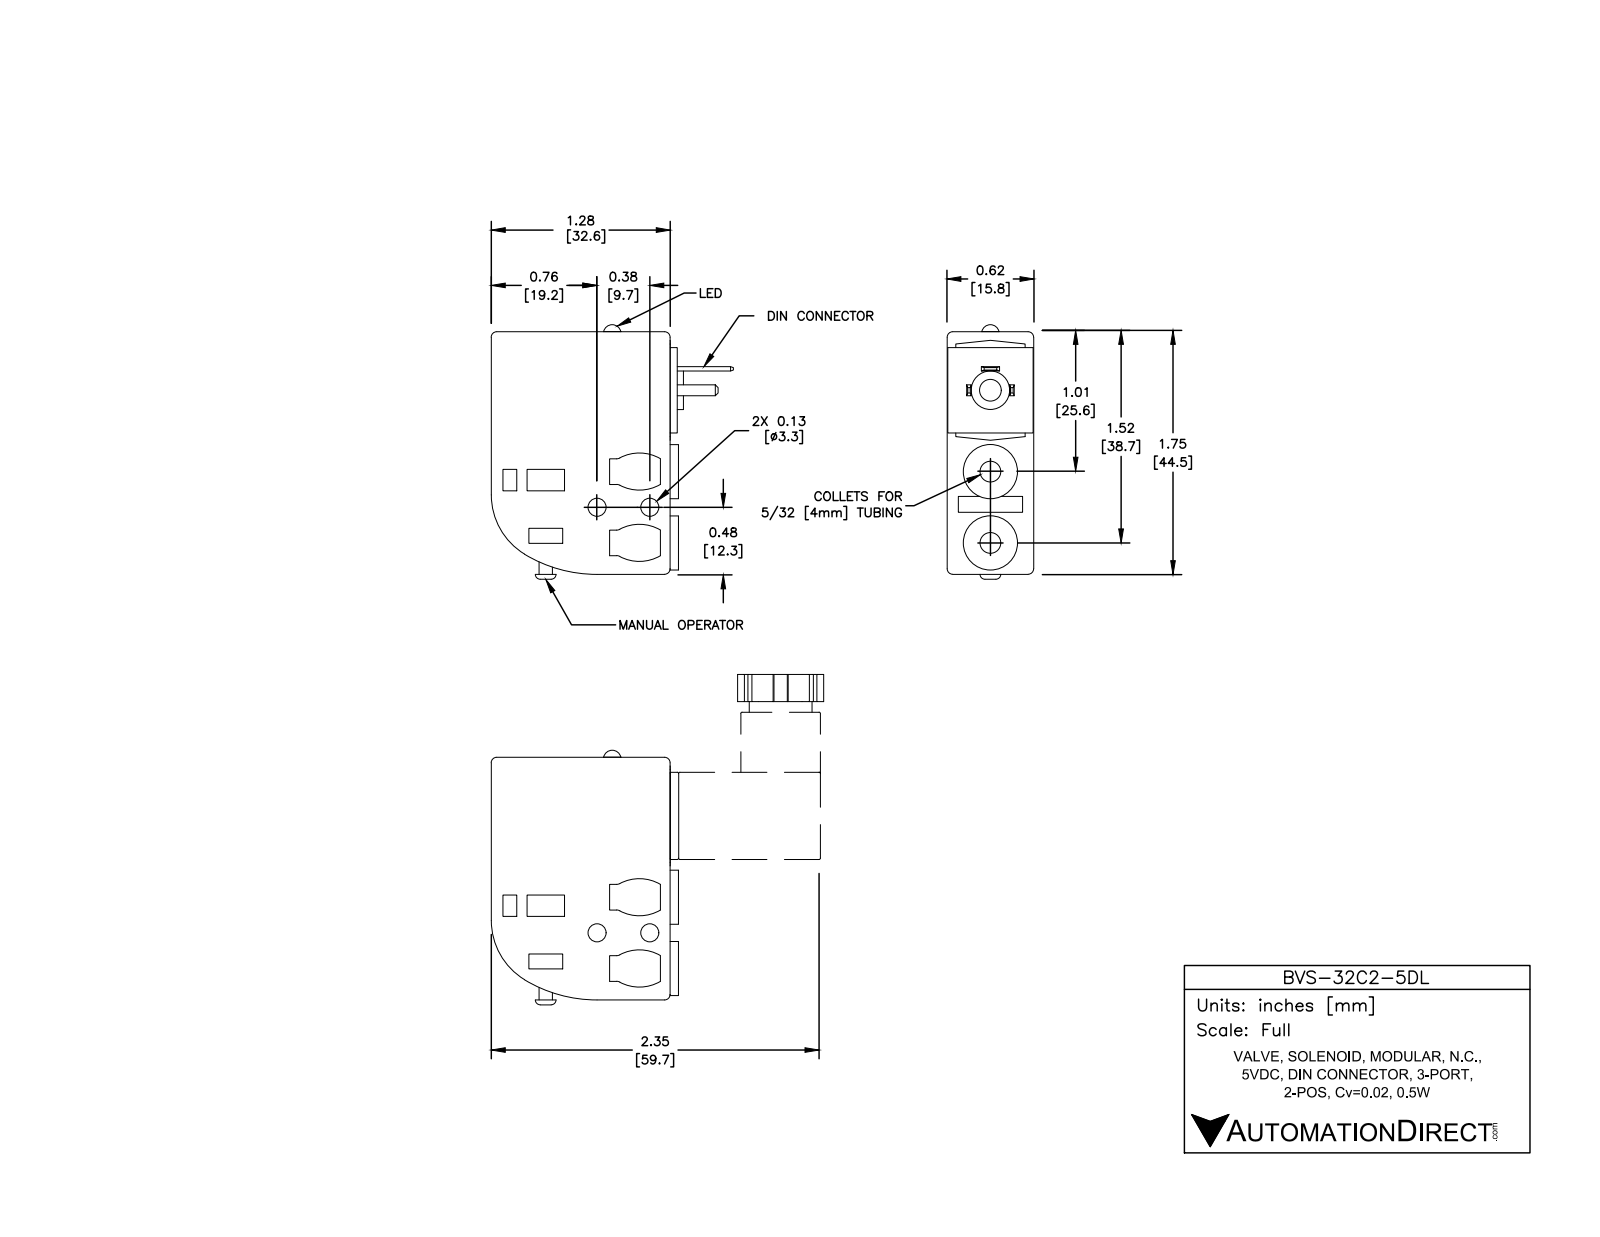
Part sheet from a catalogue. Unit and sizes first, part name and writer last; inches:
Units: inches
Overall size (bounding box): 1.84 × 1.75 × 0.62
Round holes (diameter × count): ⌀0.13 ×2, ⌀0.15 ×2, ⌀0.25 ×2, ⌀0.05 ×1, ⌀0.16 ×1
Round bosses / shafts (diameter × count): ⌀0.39 ×2, ⌀0.28 ×1, ⌀0.1 ×1
Partial cylindrical surfaces — rounded edges, fillets, slot ends (radius × count): R0.05 ×4, R0.3 ×4, R0.04 ×3, R0.5 ×1, R1 ×1
Main face-to-face distances: 0.62, 0.1, 1.29, 0.52, 1.341, 0.051, 1.75, 1, 0.15, 0.06
Hole centre spacings: 0.06, 0.38, 0.45, 0.51, 0.59, 0.65, 1.1
Volume: 1.279 in³ · Surface area: 10.75 in²
Bodies: 1 solid, 162 faces (112 planar, 46 cylindrical, 4 other)
Part name (STEP PRODUCT): BVS-32C2-5DL
STEP written by: SolidWorks 2016 (AUTOMOTIVE_DESIGN)
